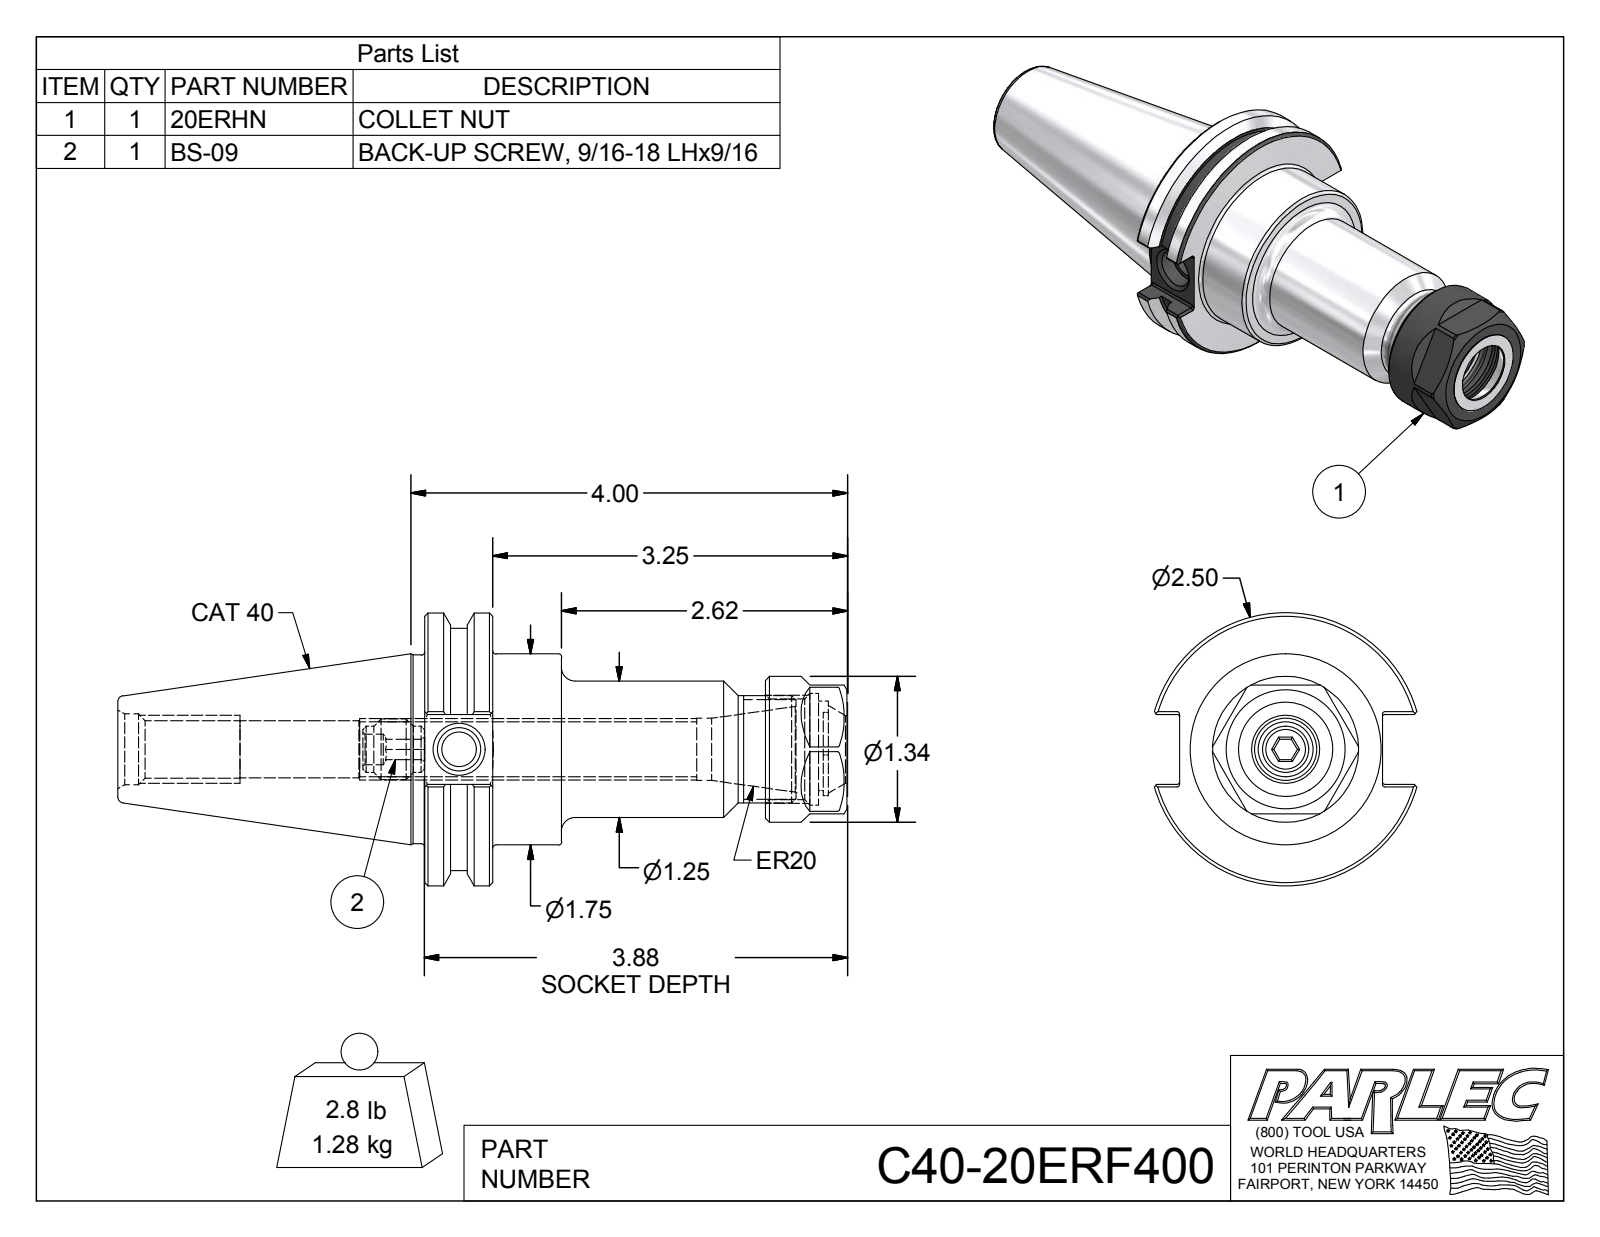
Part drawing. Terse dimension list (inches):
name: C40-20ER4-1; 20ERHN; BS-09; C40-20ERF400
written by: Autodesk Inventor 2016 (AUTOMOTIVE_DESIGN)
unit: in
bodies: 3 solids, 147 faces (64 planar, 40 cylindrical, 43 other)
size: 6.69 × 2.5 × 2.404
volume: 9.936 in³; area: 55.26 in²
holes: 1× ⌀0.281, 1× ⌀0.315, 1× ⌀0.399, 1× ⌀0.502, 1× ⌀0.525, 1× ⌀0.527, 1× ⌀0.57, 1× ⌀0.61, 1× ⌀0.648, 1× ⌀0.925, 1× ⌀1.024
bosses: 1× ⌀2.5, 1× ⌀2.219, 1× ⌀1.75, 1× ⌀1.73, 1× ⌀1.339, 1× ⌀1.25, 1× ⌀0.984, 1× ⌀0.555
rounds: 12× R0.02, 1× R0.373, 1× R0.415, 1× R0.423
face distances: 0.625, 3.878, 3.253, 1.181, 1.255, 0.63, 2.623, 3.127, 2.502, 1.872
